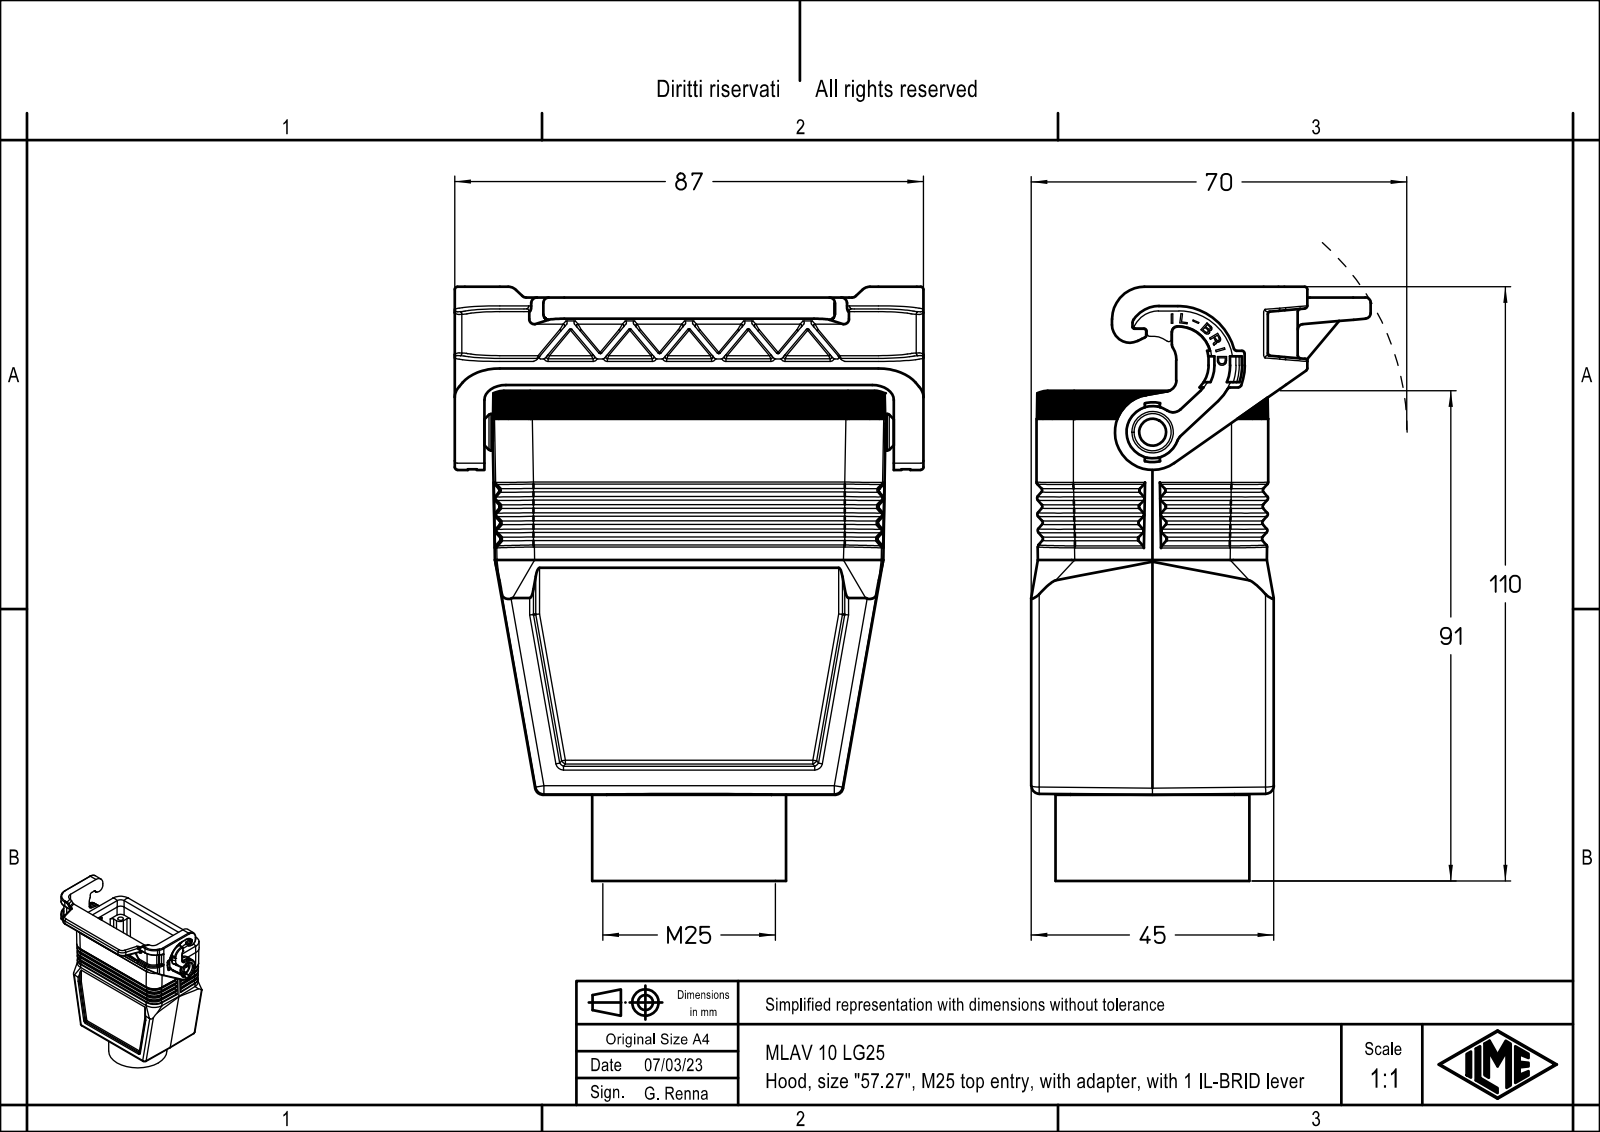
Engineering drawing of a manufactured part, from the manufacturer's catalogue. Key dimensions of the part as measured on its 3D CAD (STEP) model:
Part name (STEP PRODUCT): MLAV 10 LG32; MLAV 10 LG25
STEP written by: Creo Elements/Direct Modeling 20.1B 02-Apr-2019 (C) Parametric Technology GmbH (AUTOMOTIVE_DESIGN)
Units: millimetres
Bodies: 1 solid, 1233 faces (712 planar, 313 cylindrical, 208 other)
Overall size (bounding box): 110.25 × 87 × 63
Volume: 98 615 mm³ · Surface area: 50 099 mm²
Round holes (diameter × count): ⌀3 ×4, ⌀3.5 ×4, ⌀3.25 ×1, ⌀5.4 ×1, ⌀7.7 ×1, ⌀23.5 ×1, ⌀30.6 ×1
Round bosses / shafts (diameter × count): ⌀36 ×1, ⌀32 ×1, ⌀30.5 ×1, ⌀6.9 ×1, ⌀6.8 ×1, ⌀5.2 ×1, ⌀3.2 ×1
Partial cylindrical surfaces — rounded edges, fillets, slot ends (radius × count): R0.1 ×27, R0.5 ×25, R1.5 ×25, R0.2 ×15, R1 ×14, R7 ×14, R0.33 ×13, R3 ×12
Main face-to-face distances: 39.25, 3.75, 1, 43, 4.75, 7, 34.5, 38.25, 35.5, 2
Hole centre spacings: 31.54, 27, 57, 63.07
